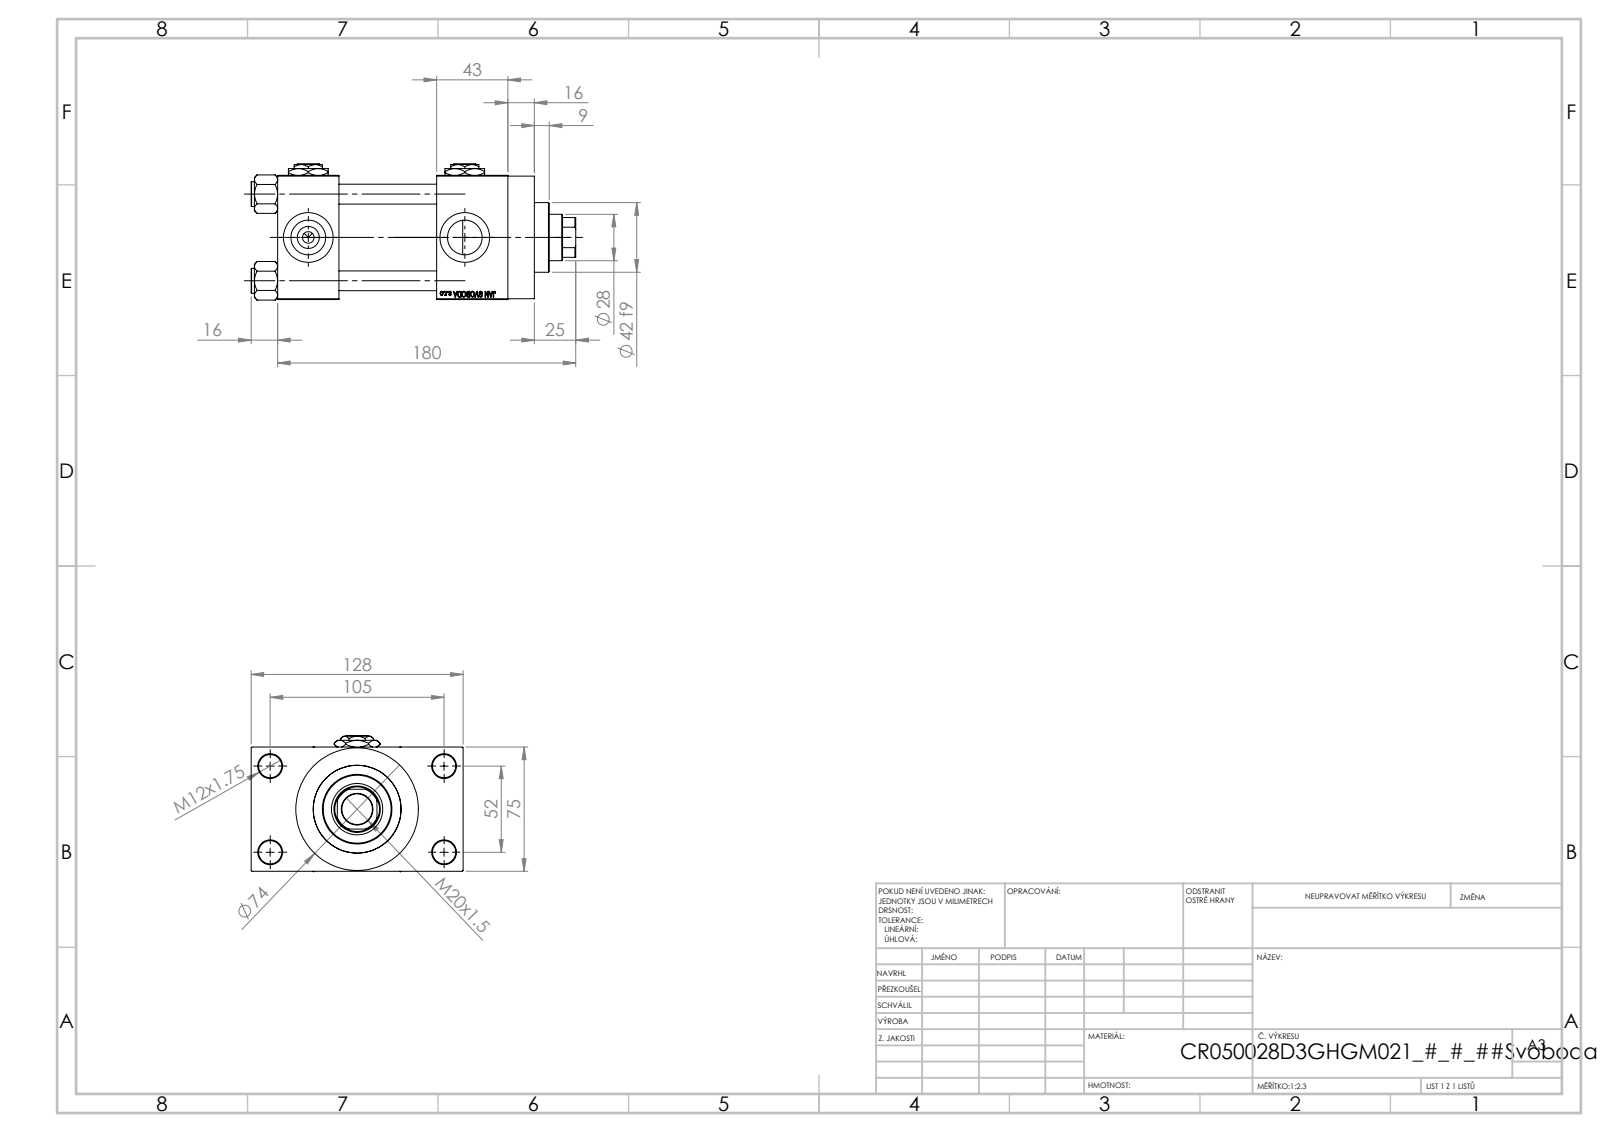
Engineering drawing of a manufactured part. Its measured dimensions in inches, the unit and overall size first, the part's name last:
Units: inches
Overall size (bounding box): 7.717 × 5.039 × 3.239
Round holes (diameter × count): ⌀0.472 ×4, ⌀0.551 ×4, ⌀0.825 ×4, ⌀1.181 ×4, ⌀0.276 ×3, ⌀0.728 ×1, ⌀1.102 ×1, ⌀1.22 ×1, ⌀1.614 ×1, ⌀1.969 ×1, ⌀2.087 ×1
Round bosses / shafts (diameter × count): ⌀0.591 ×4, ⌀2.913 ×1, ⌀2.205 ×1, ⌀1.654 ×1
Partial cylindrical surfaces — rounded edges, fillets, slot ends (radius × count): R0.531 ×1
Main face-to-face distances: 2.953, 2.323, 1.457, 3.78, 1.043, 5.472, 4.016, 1.693, 3.996, 0.63
Hole centre spacings: 1.037, 1.456, 2.059, 2.3, 2.307, 3.096, 3.715, 2.047
Volume: 49.03 in³ · Surface area: 271.9 in²
Bodies: 13 solids, 1204 faces (545 planar, 99 cylindrical, 560 other)
Part name (STEP PRODUCT): V215CR_D_TYCINKA; V215CR_VCP_D; Zatka_pro_OIL_PORT; NUT_M5_D (+2 more)
STEP written by: SolidWorks 2019 (CONFIG_CONTROL_DESIGN)
